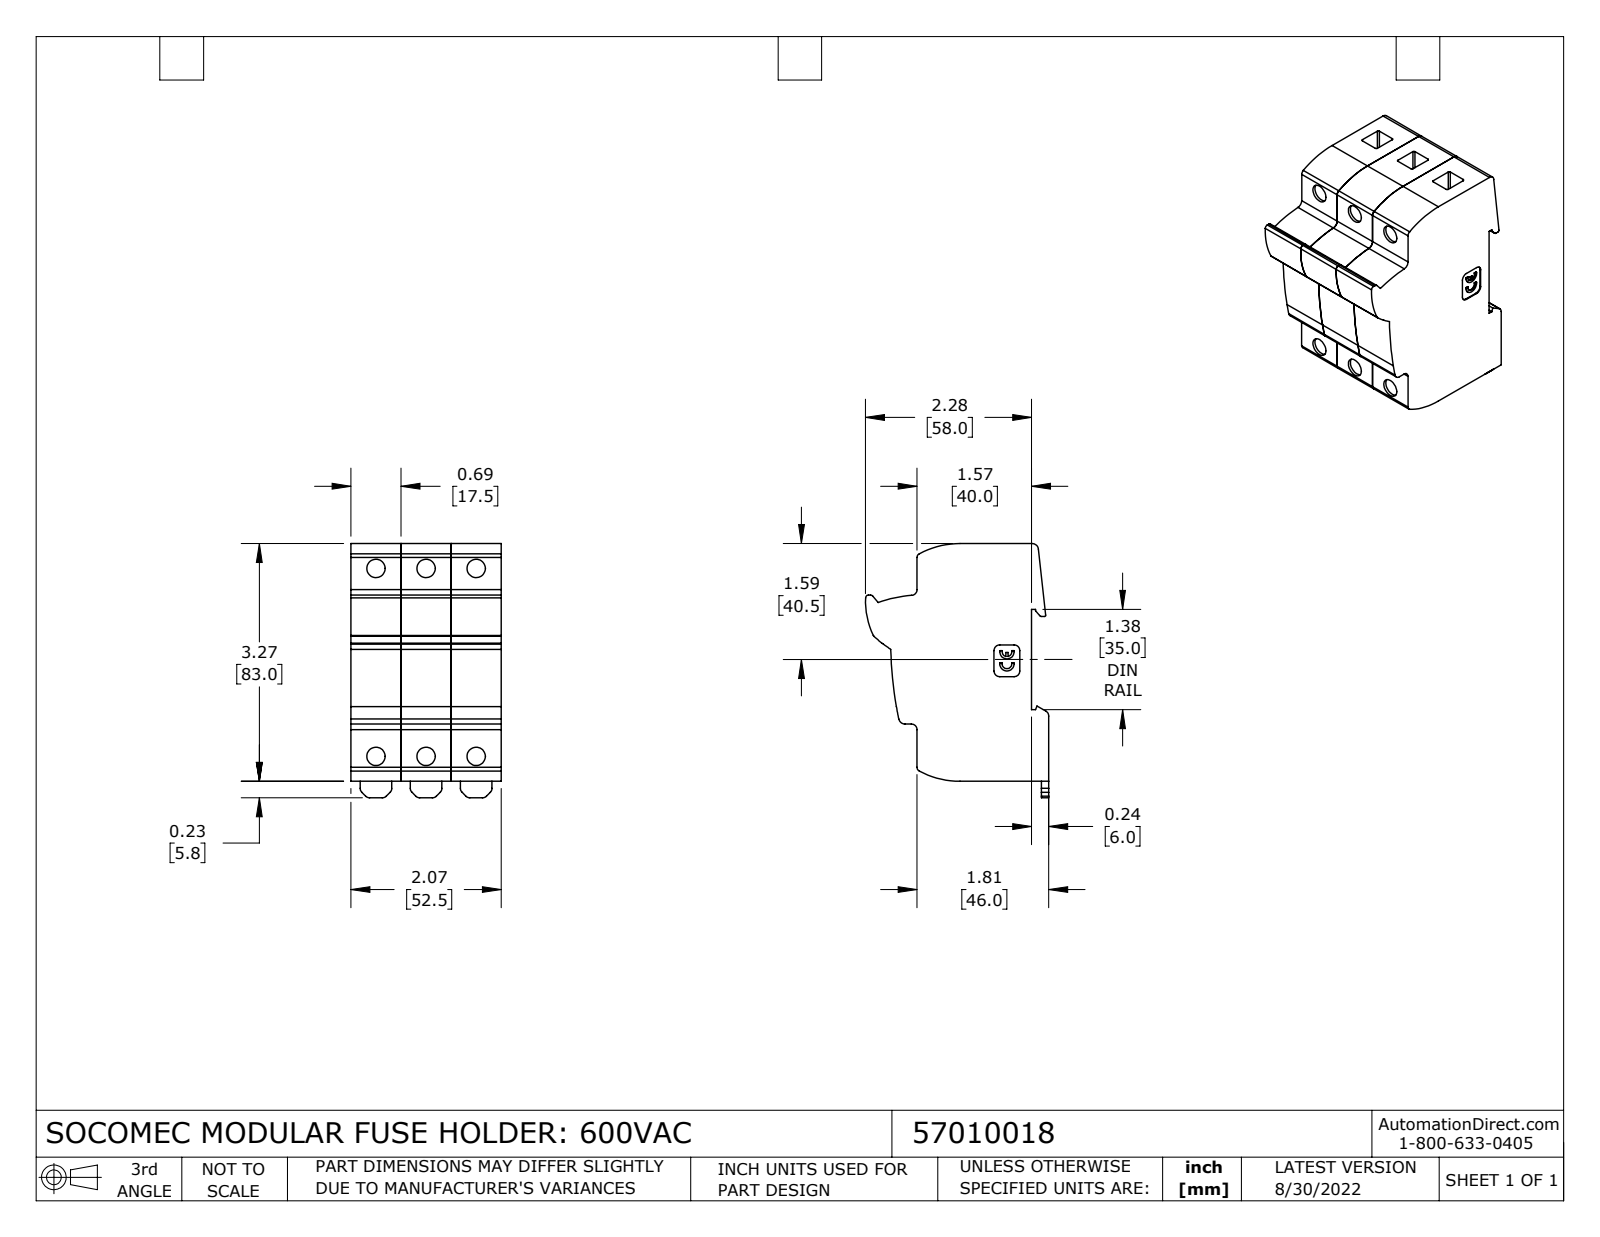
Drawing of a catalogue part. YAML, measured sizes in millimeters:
part_name: "57010018"
step_written_by: "SolidWorks 2021 (CONFIG_CONTROL_DESIGN)"
units: millimeters
bodies: {solids: 3, faces: 315, planar: 156, cylindrical: 159, other: 0}
overall_size: [88.8, 64, 52.5]
volume: 208000
surface_area: 41290
round_holes:
  - {diameter: 6.4, count: 6}
partial_cylinders:
  - {radius: 2, count: 19}
  - {radius: 0.5, count: 13}
  - {radius: 1, count: 4}
  - {radius: 1.5, count: 2}
  - {radius: 1.7, count: 2}
  - {radius: 2.2, count: 2}
  - {radius: 2.5, count: 2}
  - {radius: 30.1, count: 2}
face_to_face_distances: [17.5, 35, 52.5, 6, 40, 83, 46, 5.1, 12.4, 22.6]
hole_center_spacings: [17.5, 67.9, 65.6, 35, 74.3]
